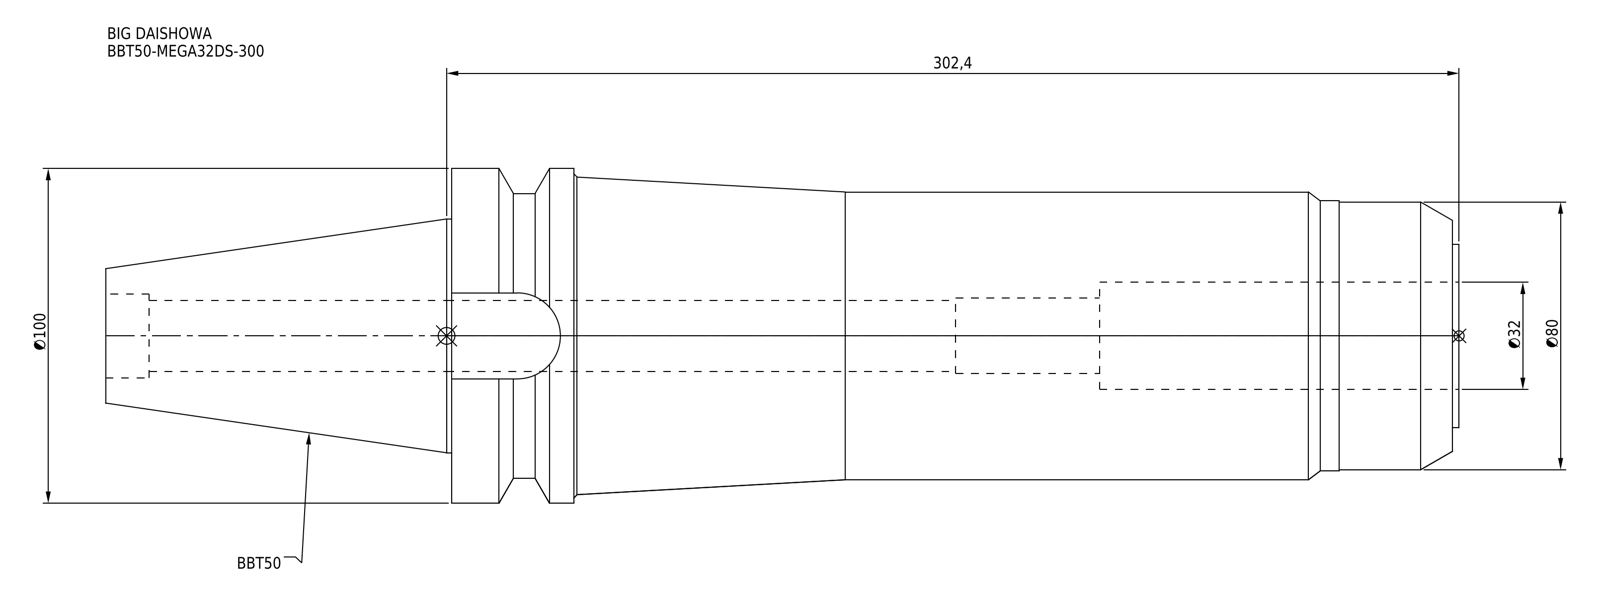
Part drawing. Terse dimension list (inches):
name: BBT50-MEGA32DS-300
written by: CREO PARAMETRIC BY PTC INC, 2016380 (AUTOMOTIVE_DESIGN)
unit: in
bodies: 1 solid, 57 faces (15 planar, 28 cylindrical, 14 other)
size: 15.913 × 3.937 × 3.937
volume: 112.6 in³; area: 223.5 in²
holes: 1× ⌀0.835, 1× ⌀0.886, 1× ⌀0.984, 1× ⌀1.26
bosses: 1× ⌀3.937, 1× ⌀3.386, 1× ⌀3.346, 1× ⌀3.177, 1× ⌀3.15, 1× ⌀2.75, 1× ⌀2.154
rounds: 1× R0.506
face distances: 11.846, 0.079, 11.768, 15.913, 15.835, 4.067, 2.787, 10.409, 10.331, 1.437
